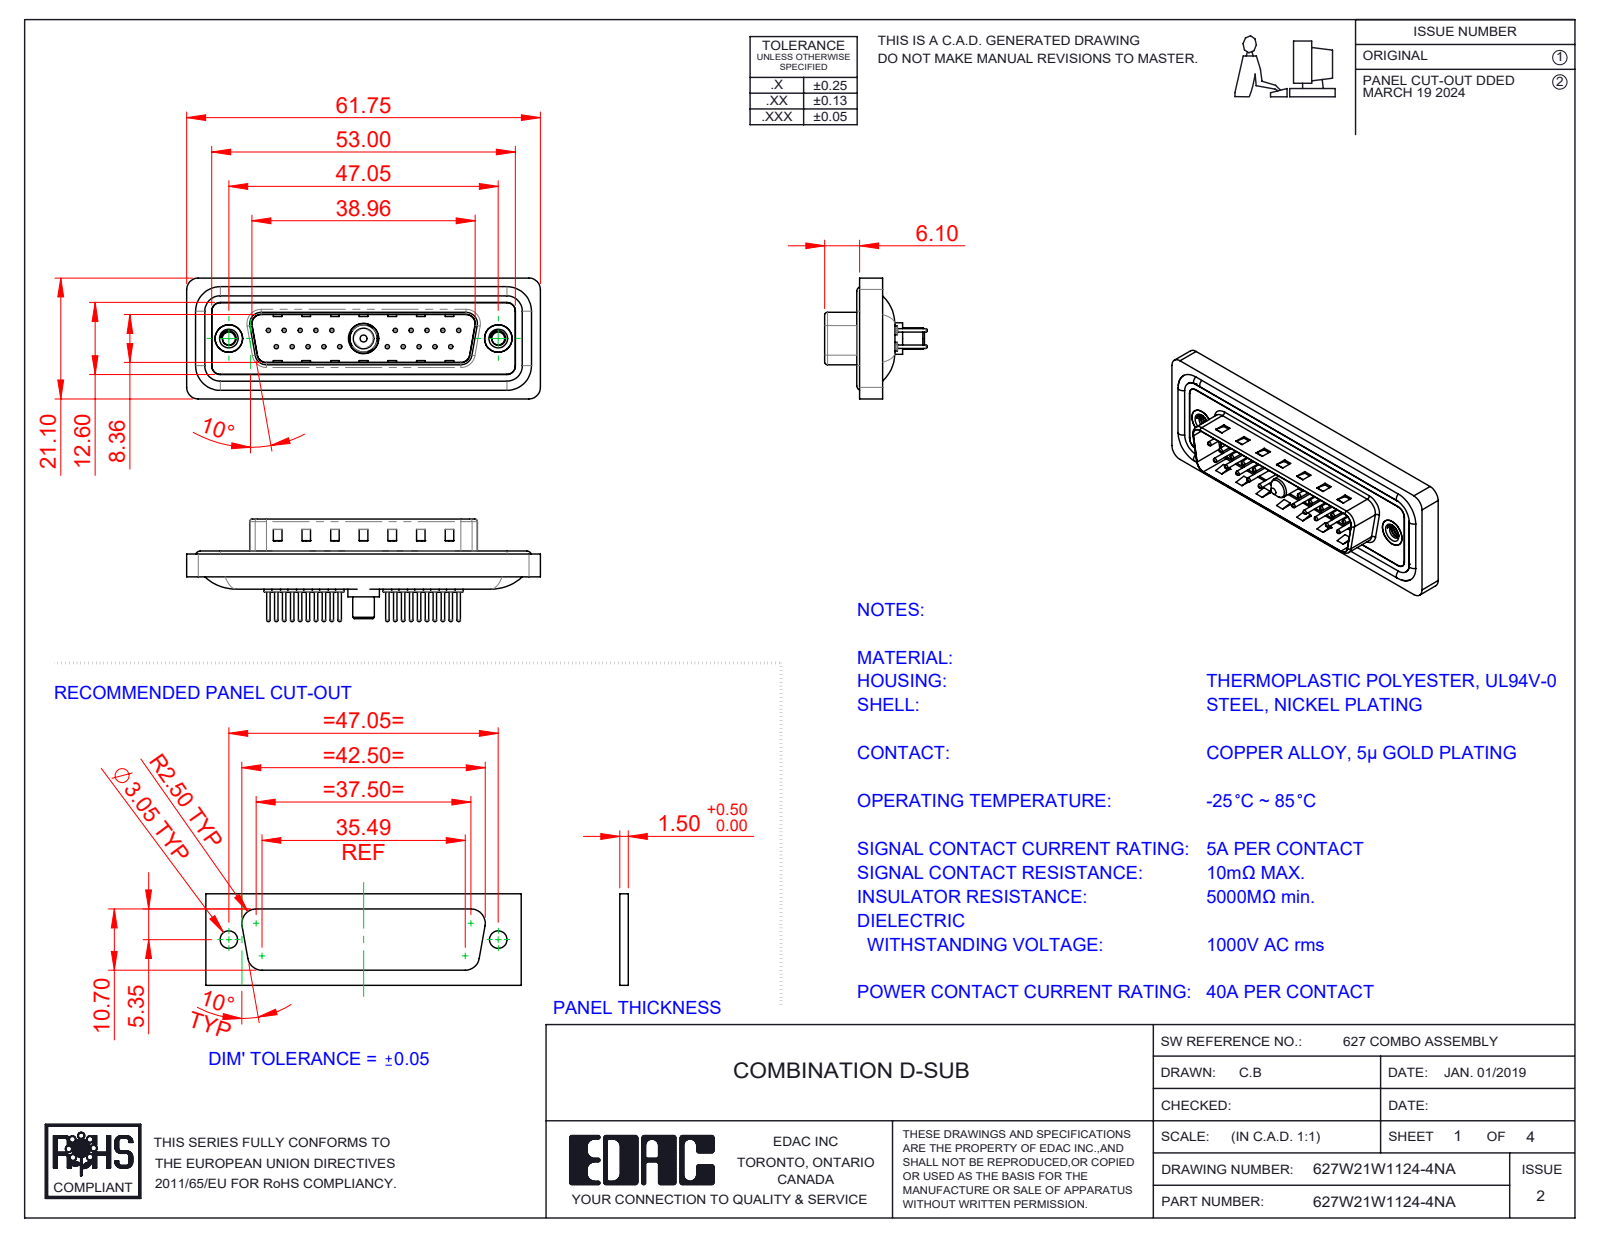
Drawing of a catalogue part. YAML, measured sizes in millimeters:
part_name: "627Combo Shell Rear_25 Contacts; 627Combo Contact Row 1_24; 627Combo Threaded Rivet_A; Power Pin_40A S (+5 more)"
step_written_by: "SolidWorks 2023 (CONFIG_CONTROL_DESIGN)"
units: millimeters
bodies: {solids: 29, faces: 1260, planar: 359, cylindrical: 489, other: 412}
overall_size: [61.75, 21.1, 17.9]
volume: 7218
surface_area: 11962
round_holes:
  - {diameter: 0.75, count: 20}
  - {diameter: 1.6, count: 20}
  - {diameter: 2, count: 20}
  - {diameter: 2.26, count: 2}
  - {diameter: 4, count: 2}
  - {diameter: 4.8, count: 2}
  - {diameter: 5, count: 2}
  - {diameter: 4.85, count: 1}
  - {diameter: 5.3, count: 1}
round_bosses_or_shafts:
  - {diameter: 1.5, count: 20}
  - {diameter: 0.6, count: 20}
  - {diameter: 1.6, count: 4}
  - {diameter: 4.9, count: 2}
  - {diameter: 5.5, count: 1}
  - {diameter: 5.2, count: 1}
  - {diameter: 4.75, count: 1}
  - {diameter: 3.75, count: 1}
partial_cylinders:
  - {radius: 1.5, count: 22}
  - {radius: 2, count: 18}
  - {radius: 0.5, count: 8}
  - {radius: 1.6, count: 8}
  - {radius: 0.25, count: 4}
  - {radius: 0.6, count: 4}
  - {radius: 0.65, count: 4}
  - {radius: 0.9, count: 4}
face_to_face_distances: [0.4, 1.5, 1.1, 1.6, 0.5, 3.1, 2.9, 4.1, 0.82, 9.58]
hole_center_spacings: [3.16, 2.77, 5.54, 8.31, 5.04, 19.39, 20.97, 22.16]
